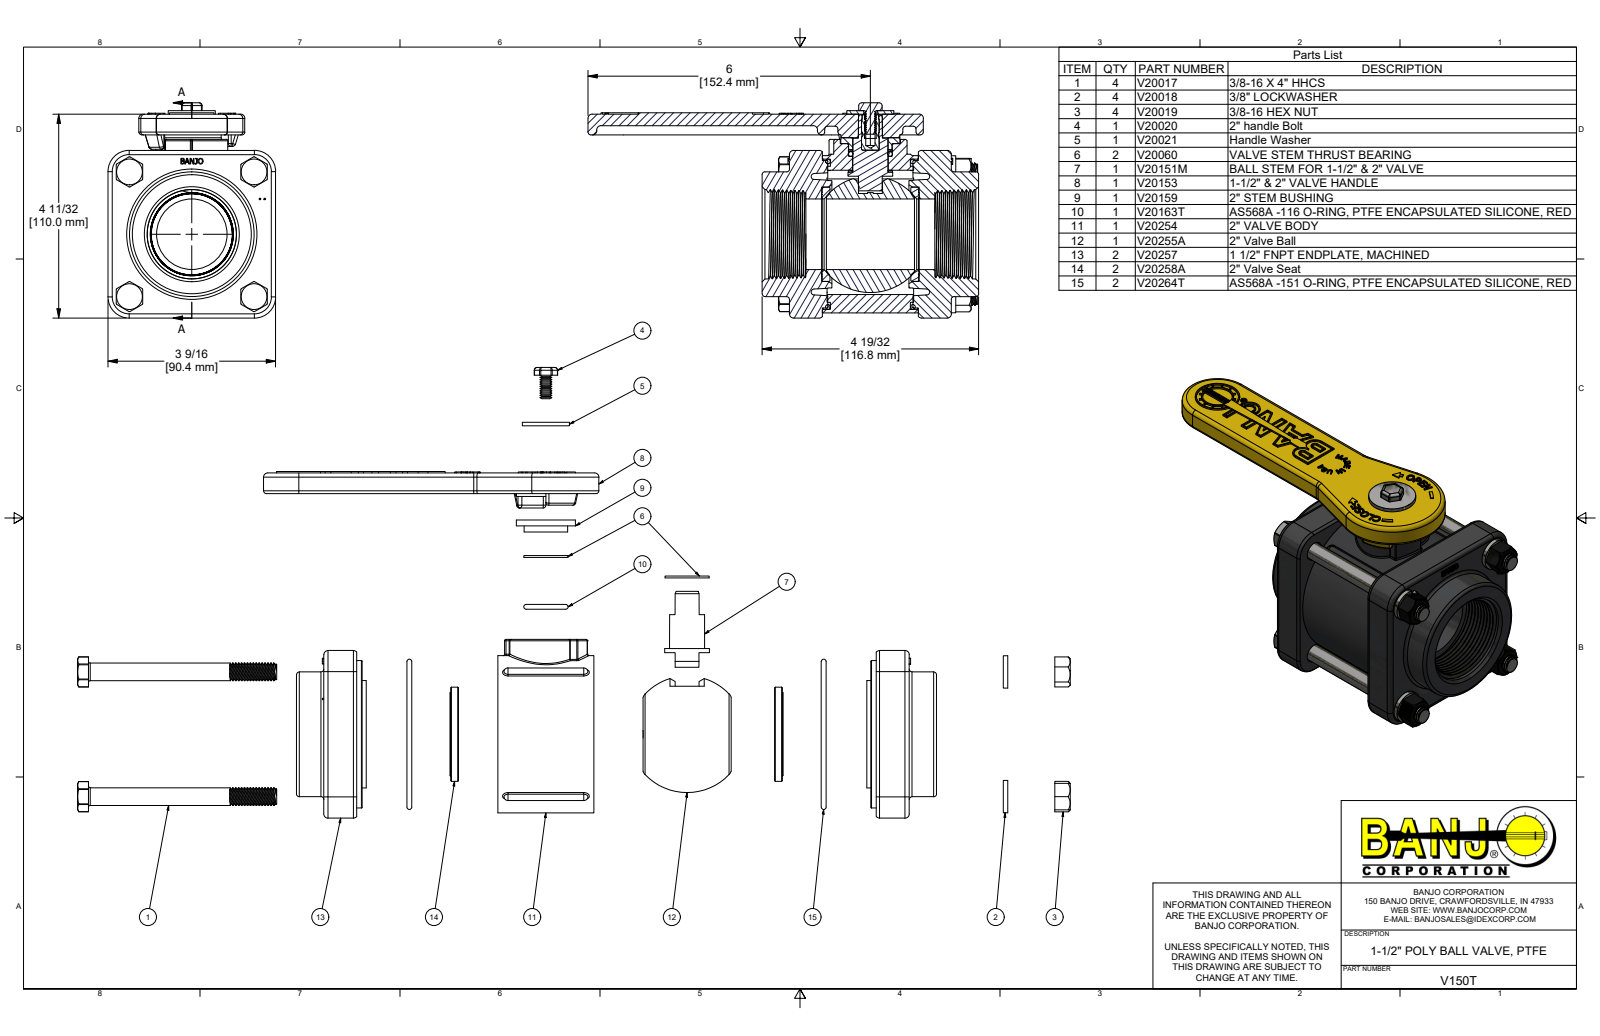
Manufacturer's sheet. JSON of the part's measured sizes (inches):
{"part_name": "V150T; V20254; V20257; VX20257 (+8 more)", "step_written_by": "Autodesk Inventor 2022 (AUTOMOTIVE_DESIGN)", "units": "inches", "bodies": {"solids": 30, "faces": 2225, "planar": 944, "cylindrical": 498, "other": 783}, "overall_size": [8.3, 4.571, 3.56], "volume_in3": 35.48, "surface_area_in2": 285.9, "round_holes": [[0.165, 10], [0.307, 4], [0.385, 4], [0.42, 4], [0.089, 1], [0.196, 1], [0.281, 1], [0.351, 1], [0.375, 1], [0.635, 1], [0.75, 1], [0.751, 1]], "round_bosses_or_shafts": [[0.324, 60], [0.687, 4], [0.375, 4], [3.34, 1], [3.13, 1], [2.89, 1], [2.65, 1], [2.28, 1]], "partial_cylinders_radius": [[0.09, 28], [0.03, 26], [0.06, 24], [0.125, 9], [0.162, 8], [0.015, 4], [0.031, 4], [0.094, 4]], "face_to_face_distances": [2.74, 0.7, 3.56, 3.44, 0.245, 0.815, 2.625, 0.115, 1.925, 2.04], "hole_center_spacings": [1.363, 2.316, 2.632, 0.705, 0.971, 1.677, 2.36, 2.813]}
